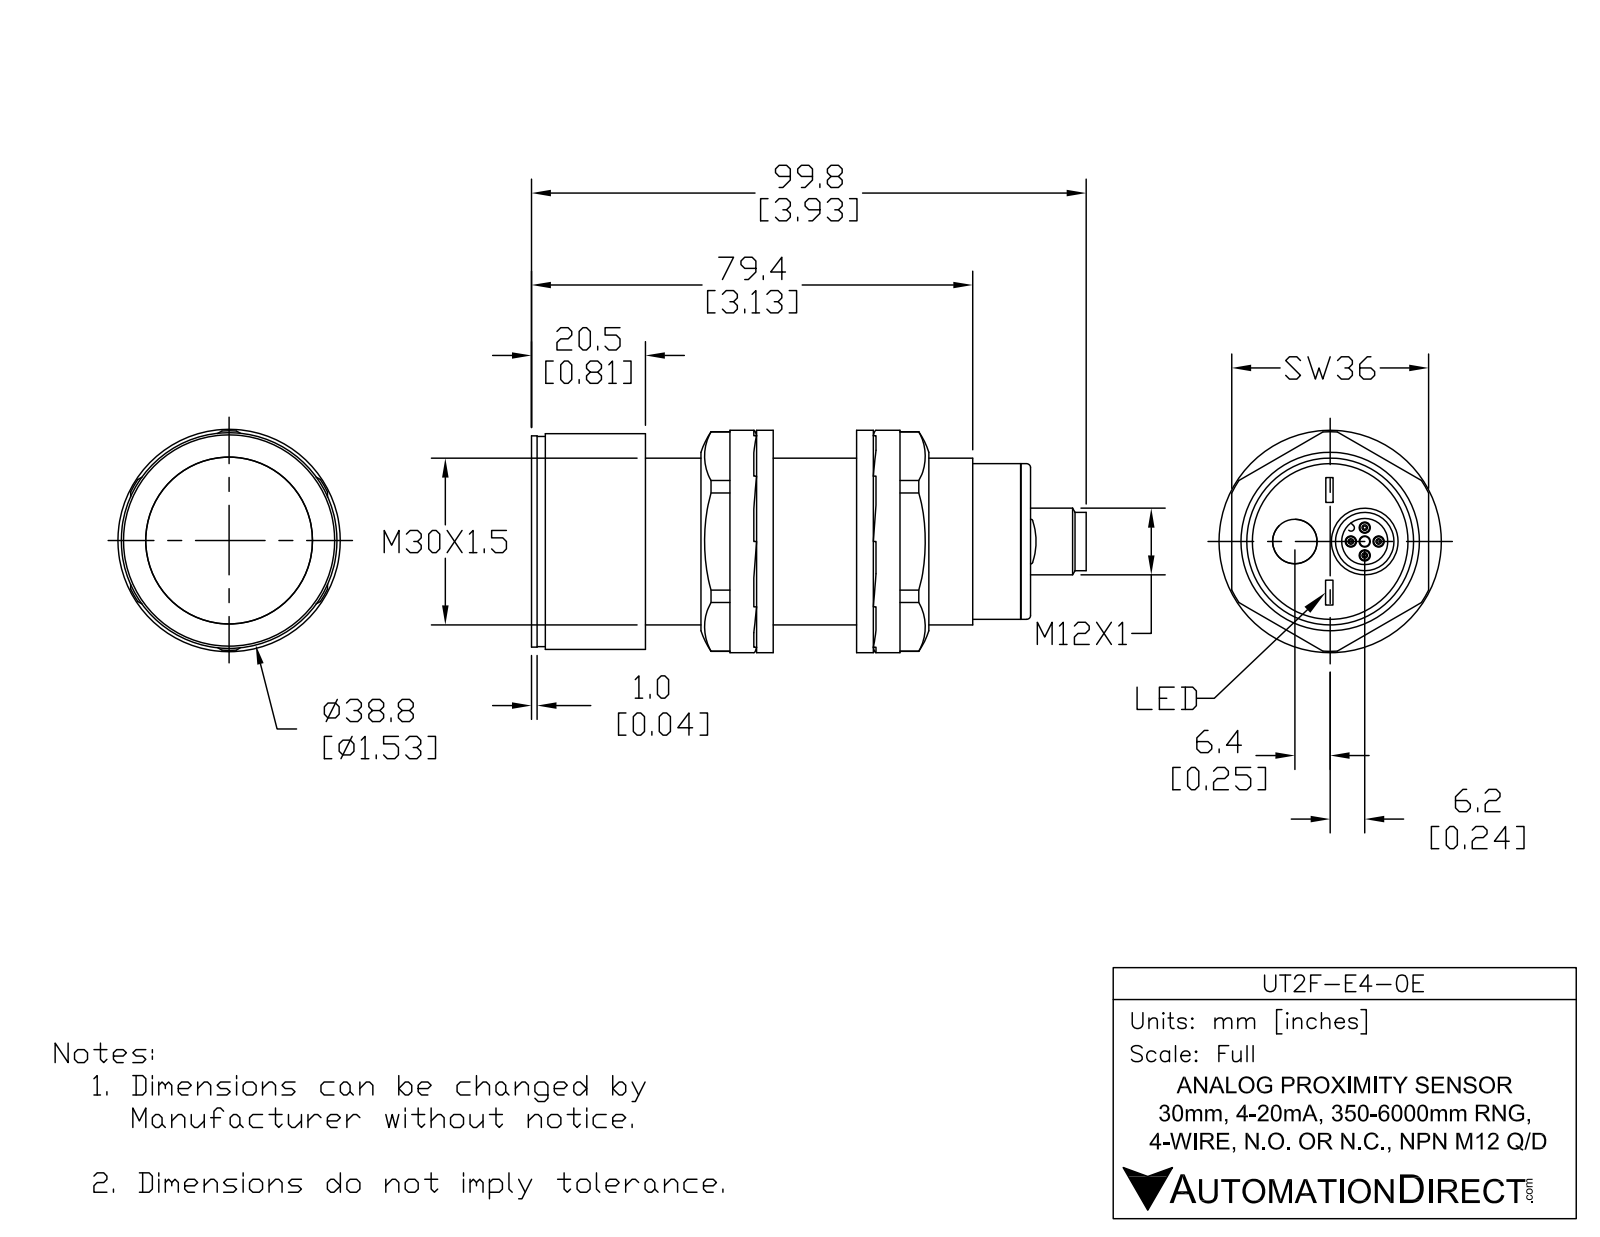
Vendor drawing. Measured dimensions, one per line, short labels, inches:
name: UT2F-E4-0E
written by: SolidWorks 2017 (AUTOMOTIVE_DESIGN)
unit: in
bodies: 5 solids, 108 faces (31 planar, 47 cylindrical, 30 other)
size: 3.894 × 1.528 × 1.528
volume: 4.372 in³; area: 24.88 in²
holes: 4× ⌀0.071, 1× ⌀0.315, 1× ⌀0.327, 1× ⌀0.372, 1× ⌀1.299
bosses: 4× ⌀0.039, 1× ⌀1.528, 1× ⌀1.488, 1× ⌀1.181, 1× ⌀1.102, 1× ⌀0.472, 1× ⌀0.413, 1× ⌀0.364
rounds: 2× R0.012, 1× R0.024
face distances: 3.37, 0.059, 3.429, 0.767, 0.709, 2.661, 0.059, 3.429, 0.071, 3.5
hole spacings: 0.098, 0.139, 0.197, 0.264, 0.505, 0.146, 0.245, 0.25
